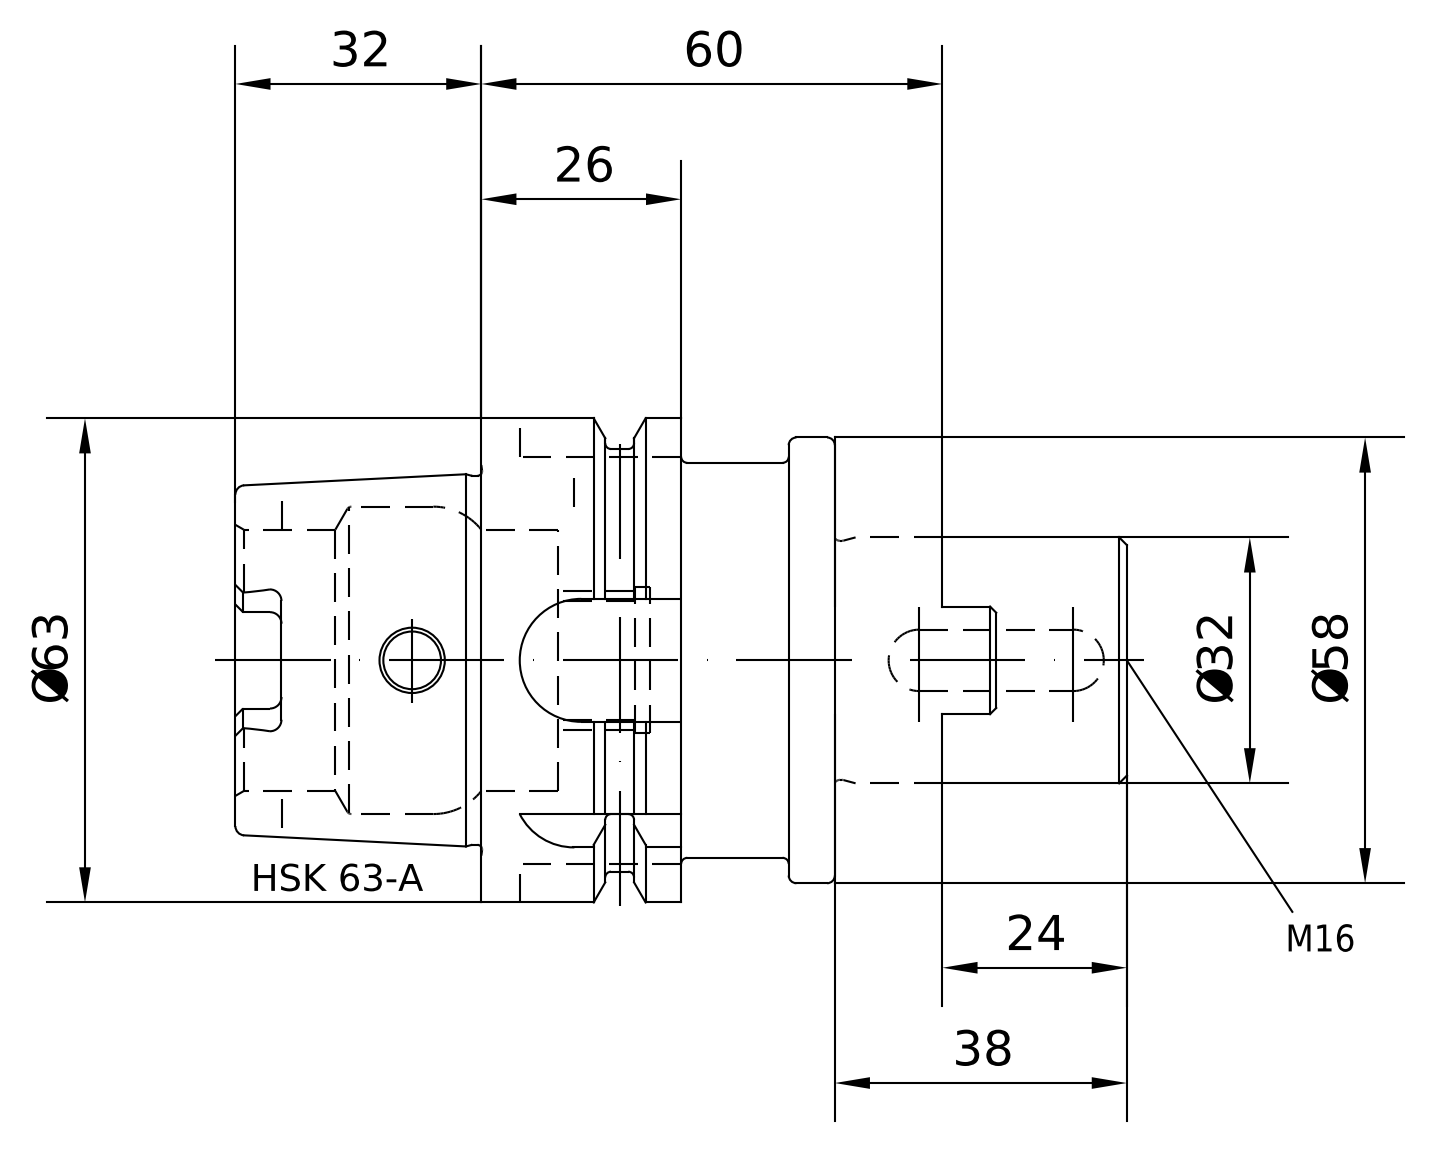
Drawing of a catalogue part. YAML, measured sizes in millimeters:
part_name: "A63-040-32; 85-200-32; A63-040-32_ASM"
step_written_by: "PRO/ENGINEER BY PARAMETRIC TECHNOLOGY CORPORATION, 2010430 (CONFIG_CONTROL_DESIGN)"
units: millimeters
bodies: {solids: 2, faces: 272, planar: 126, cylindrical: 66, other: 80}
overall_size: [116, 63, 63]
volume: 173983
surface_area: 43655
round_holes:
  - {diameter: 7.5, count: 1}
  - {diameter: 10, count: 1}
  - {diameter: 14, count: 1}
  - {diameter: 16, count: 1}
  - {diameter: 16.92, count: 1}
  - {diameter: 18.32, count: 1}
  - {diameter: 18.66, count: 1}
  - {diameter: 32.39, count: 1}
  - {diameter: 34, count: 1}
  - {diameter: 37, count: 1}
  - {diameter: 40, count: 1}
round_bosses_or_shafts:
  - {diameter: 63, count: 1}
  - {diameter: 58, count: 1}
  - {diameter: 55, count: 1}
  - {diameter: 51.4, count: 1}
  - {diameter: 48.04, count: 1}
  - {diameter: 32, count: 1}
  - {diameter: 18, count: 1}
partial_cylinders:
  - {radius: 1.5, count: 6}
  - {radius: 3, count: 4}
  - {radius: 4, count: 2}
  - {radius: 7.05, count: 1}
  - {radius: 8, count: 1}
  - {radius: 8.02, count: 1}
  - {radius: 9.02, count: 1}
face_to_face_distances: [14, 20, 46, 60, 58, 26, 34, 10, 36, 84]
